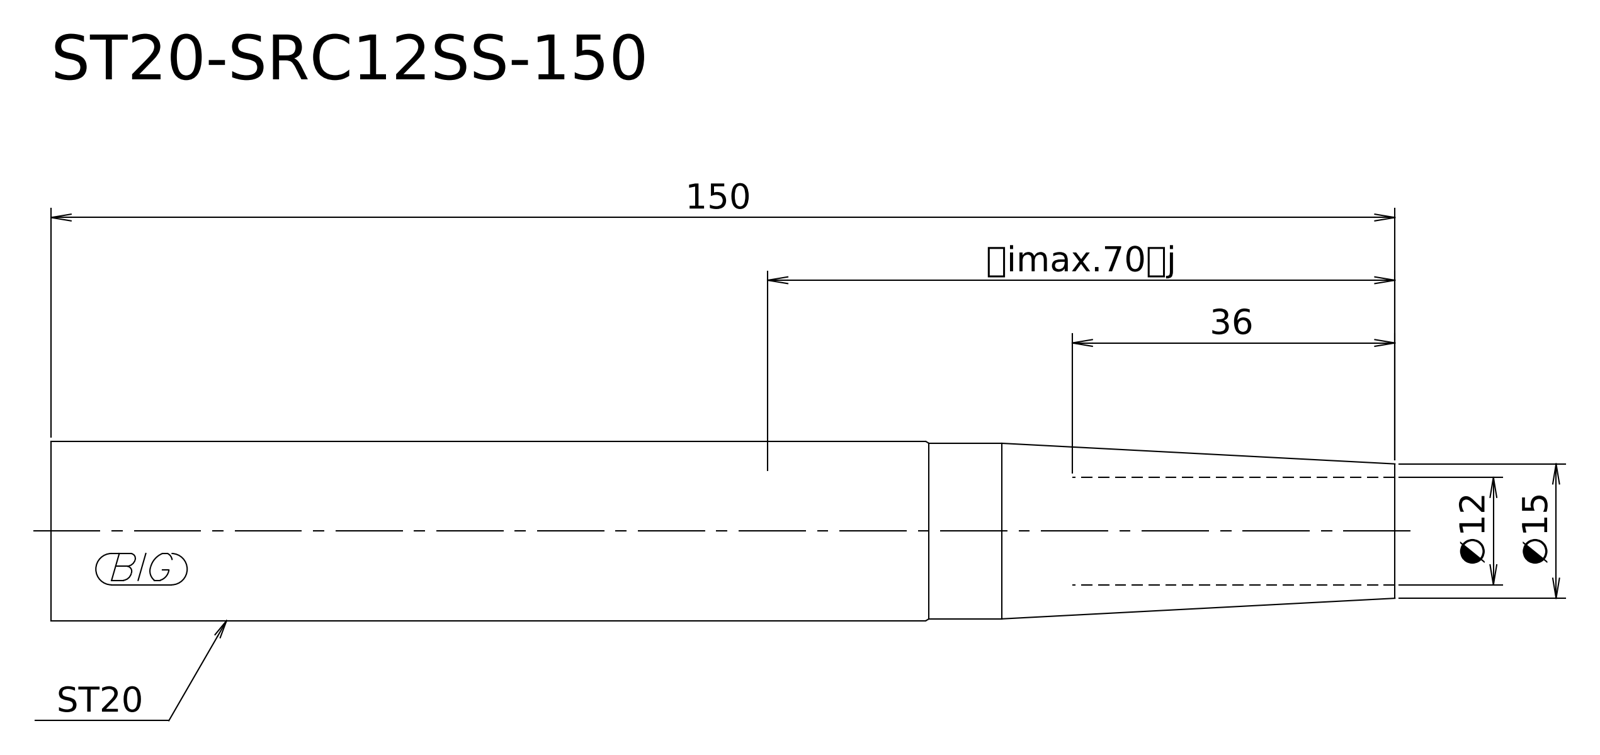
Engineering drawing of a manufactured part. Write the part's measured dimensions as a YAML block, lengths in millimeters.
step_written_by: "Kubotek KeyCreator V8.5.1 (14335) (CONFIG_CONTROL_DESIGN)"
units: millimeters
bodies: {solids: 1, faces: 6, planar: 2, cylindrical: 2, other: 2}
overall_size: [150, 20, 20]
volume: 43610
surface_area: 9540
round_bosses_or_shafts:
  - {diameter: 20, count: 1}
  - {diameter: 19.6, count: 1}
face_to_face_distances: [150]
